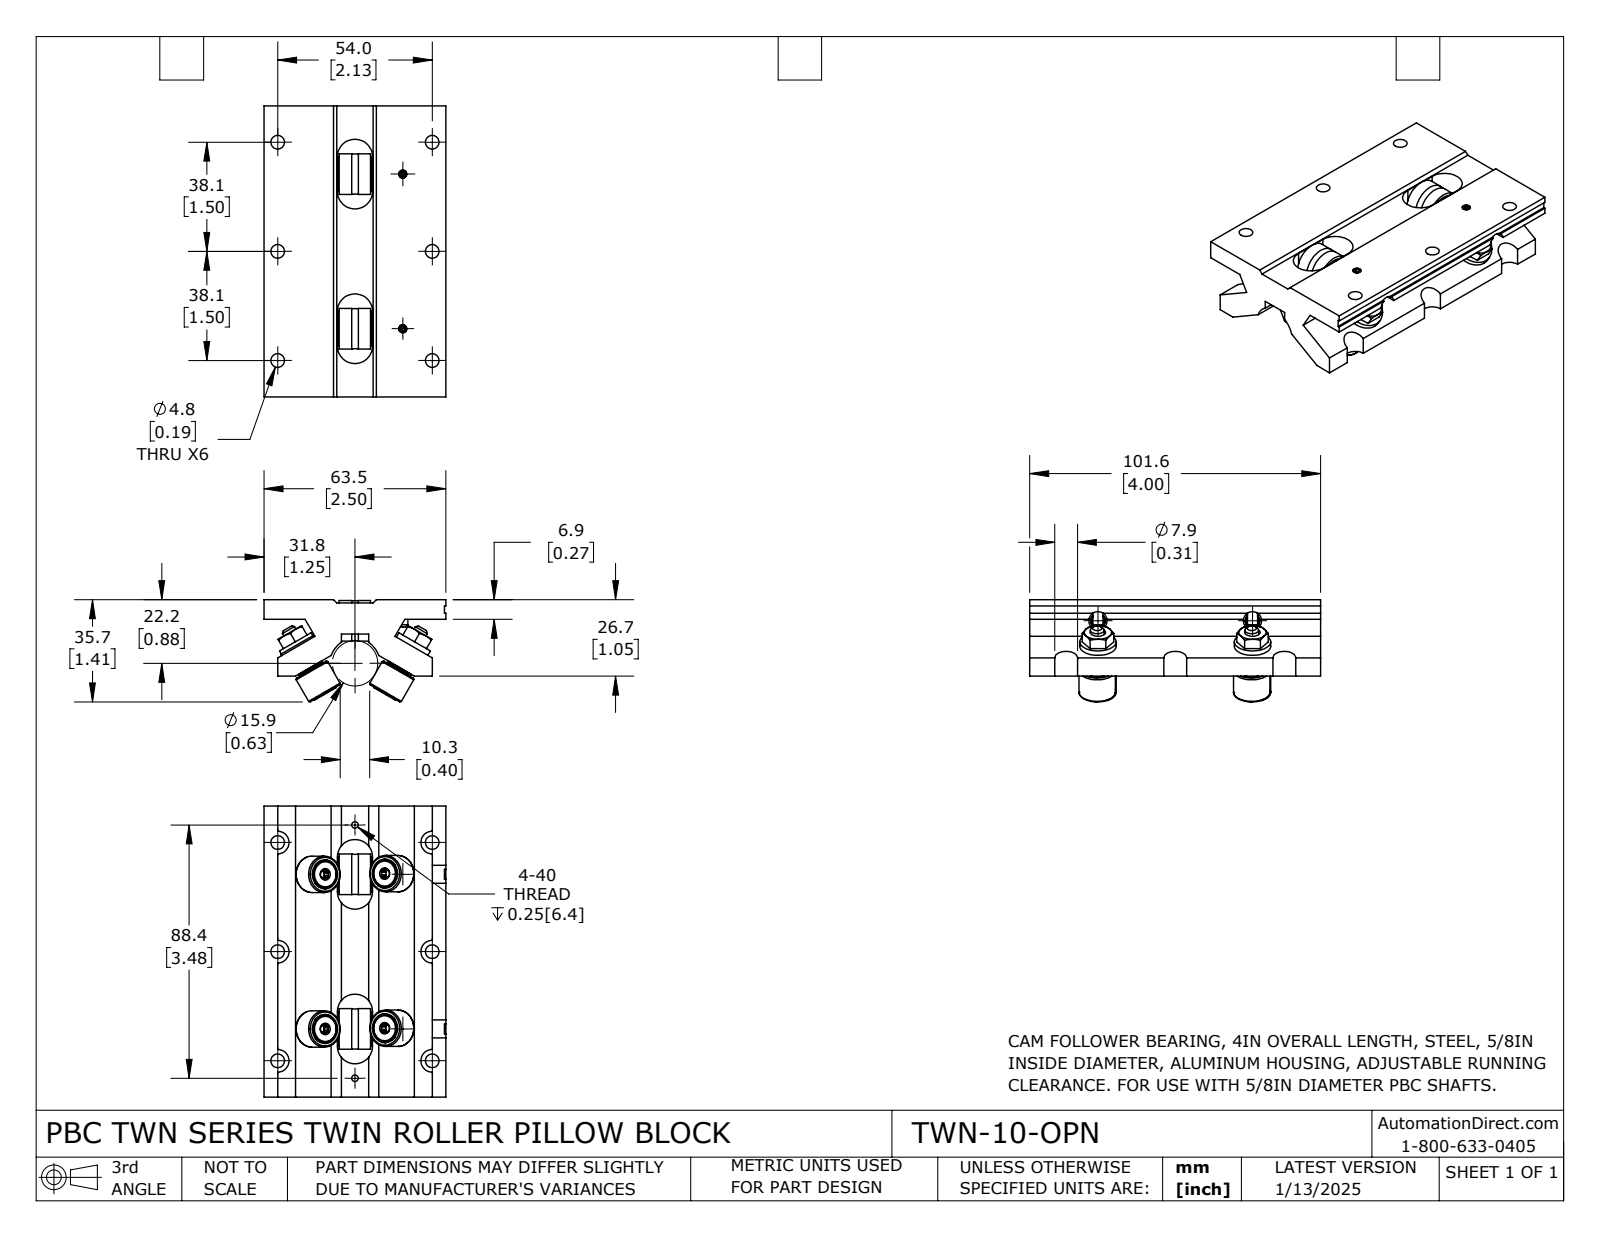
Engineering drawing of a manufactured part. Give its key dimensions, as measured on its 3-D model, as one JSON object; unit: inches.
{"part_name": "TWN-10-OPN", "step_written_by": "SolidWorks 2023 (CONFIG_CONTROL_DESIGN)", "units": "inches", "bodies": {"solids": 21, "faces": 602, "planar": 248, "cylindrical": 190, "other": 164}, "overall_size": [4, 2.5, 1.405], "volume_in3": 6.074, "surface_area_in2": 57.97, "round_holes": [[0.187, 6], [0.129, 4], [0.149, 4], [0.399, 4], [0.089, 2], [0.107, 2], [0.156, 2], [0.19, 2], [0.193, 2], [0.196, 2], [0.197, 2], [0.2, 2]], "round_bosses_or_shafts": [[0.5, 6], [0.369, 4], [0.557, 2], [0.515, 2], [0.478, 2], [0.25, 2], [0.2, 2], [0.197, 2]], "partial_cylinders_radius": [[0.156, 6], [0.242, 3], [0.243, 1], [0.344, 1]], "face_to_face_distances": [0.34, 0.27, 0.78, 1.05, 4, 2.313, 0.187, 1.005, 0.225, 0.045], "hole_center_spacings": [2.125, 1.089, 1.5, 2.039, 2.601, 3.41, 0.596, 0.944]}
